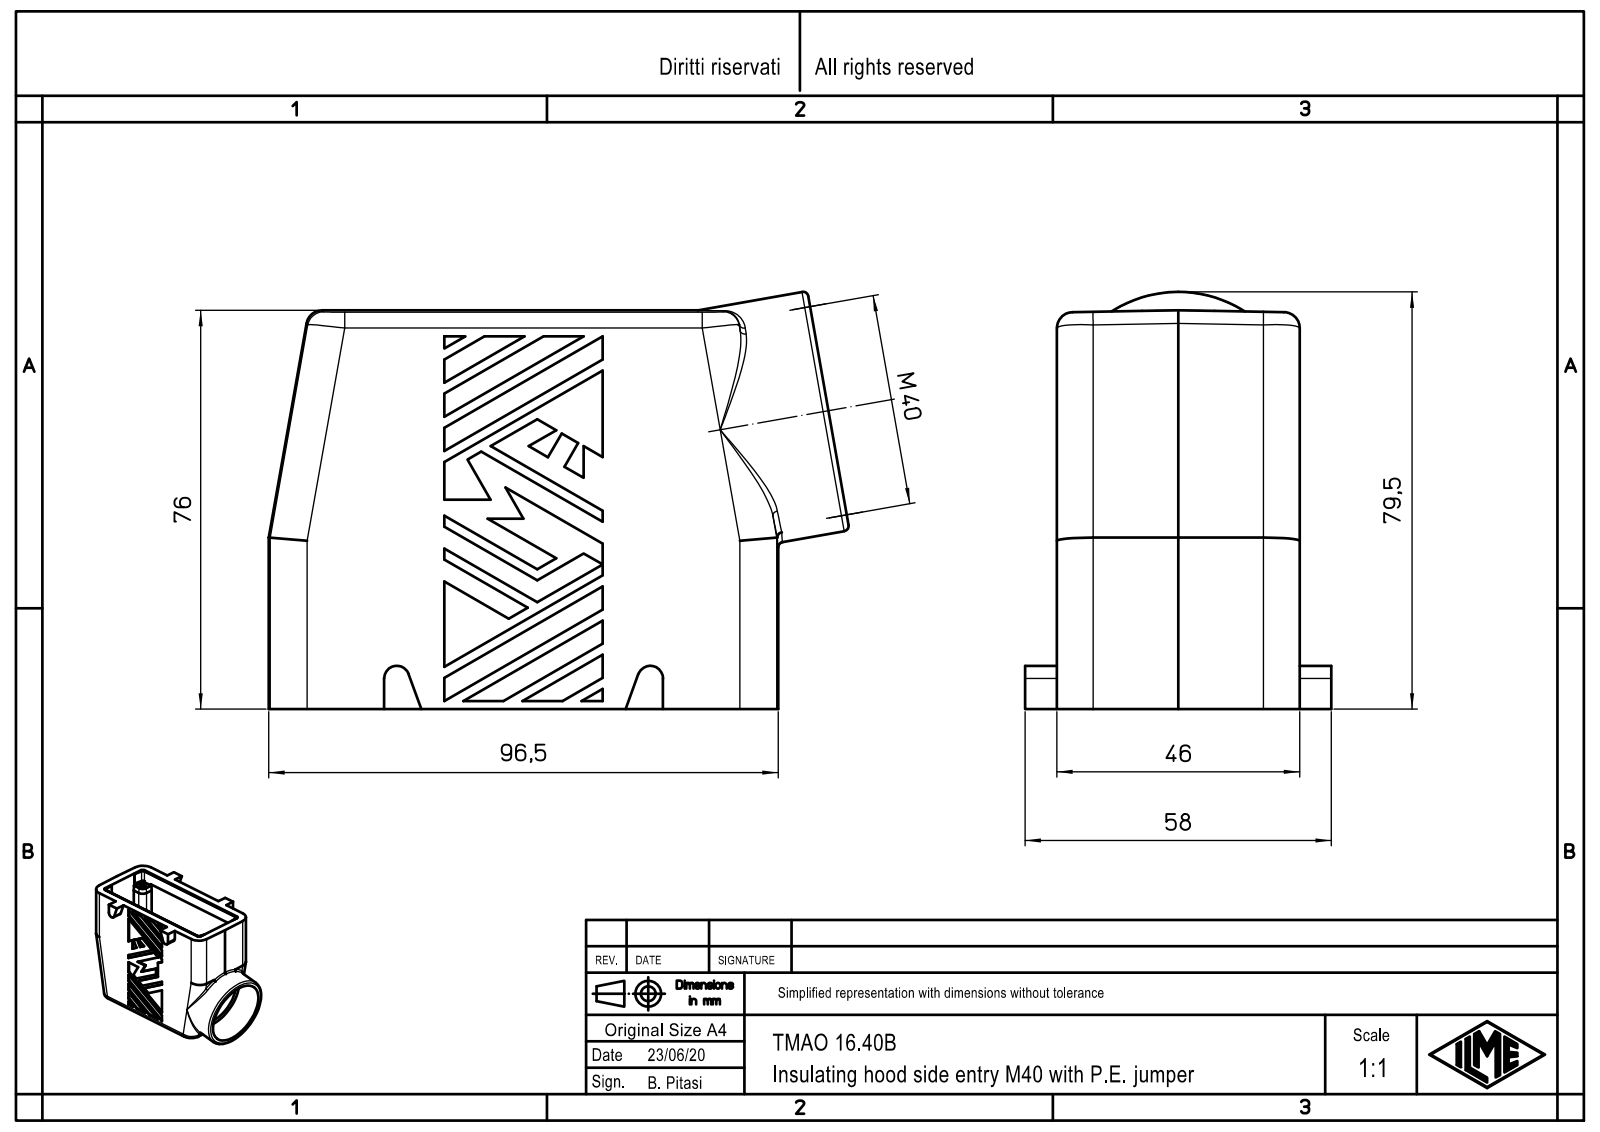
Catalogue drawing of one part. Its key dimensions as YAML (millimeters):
part_name: "TMAO_16.40B"
step_written_by: "Creo Elements/Direct Modeling 20.1B 02-Apr-2019 (C) Parametric Technology GmbH (AUTOMOTIVE_DESIGN)"
units: millimeters
bodies: {solids: 1, faces: 471, planar: 300, cylindrical: 83, other: 88}
overall_size: [109.83, 78.98, 58]
volume: 127439
surface_area: 51598
round_holes:
  - {diameter: 3, count: 4}
  - {diameter: 3.5, count: 4}
  - {diameter: 34, count: 1}
  - {diameter: 40, count: 1}
round_bosses_or_shafts:
  - {diameter: 4.8, count: 4}
  - {diameter: 46, count: 1}
partial_cylinders:
  - {radius: 1.5, count: 12}
  - {radius: 7, count: 8}
  - {radius: 3, count: 6}
  - {radius: 1.3, count: 4}
  - {radius: 1.6, count: 4}
  - {radius: 2, count: 4}
  - {radius: 3.5, count: 4}
  - {radius: 2.4, count: 2}
face_to_face_distances: [46, 0.5, 45.5, 69.99, 5.6, 45, 39.4, 5.3, 5.8, 40.2]
hole_center_spacings: [27, 77.5, 82.07]
